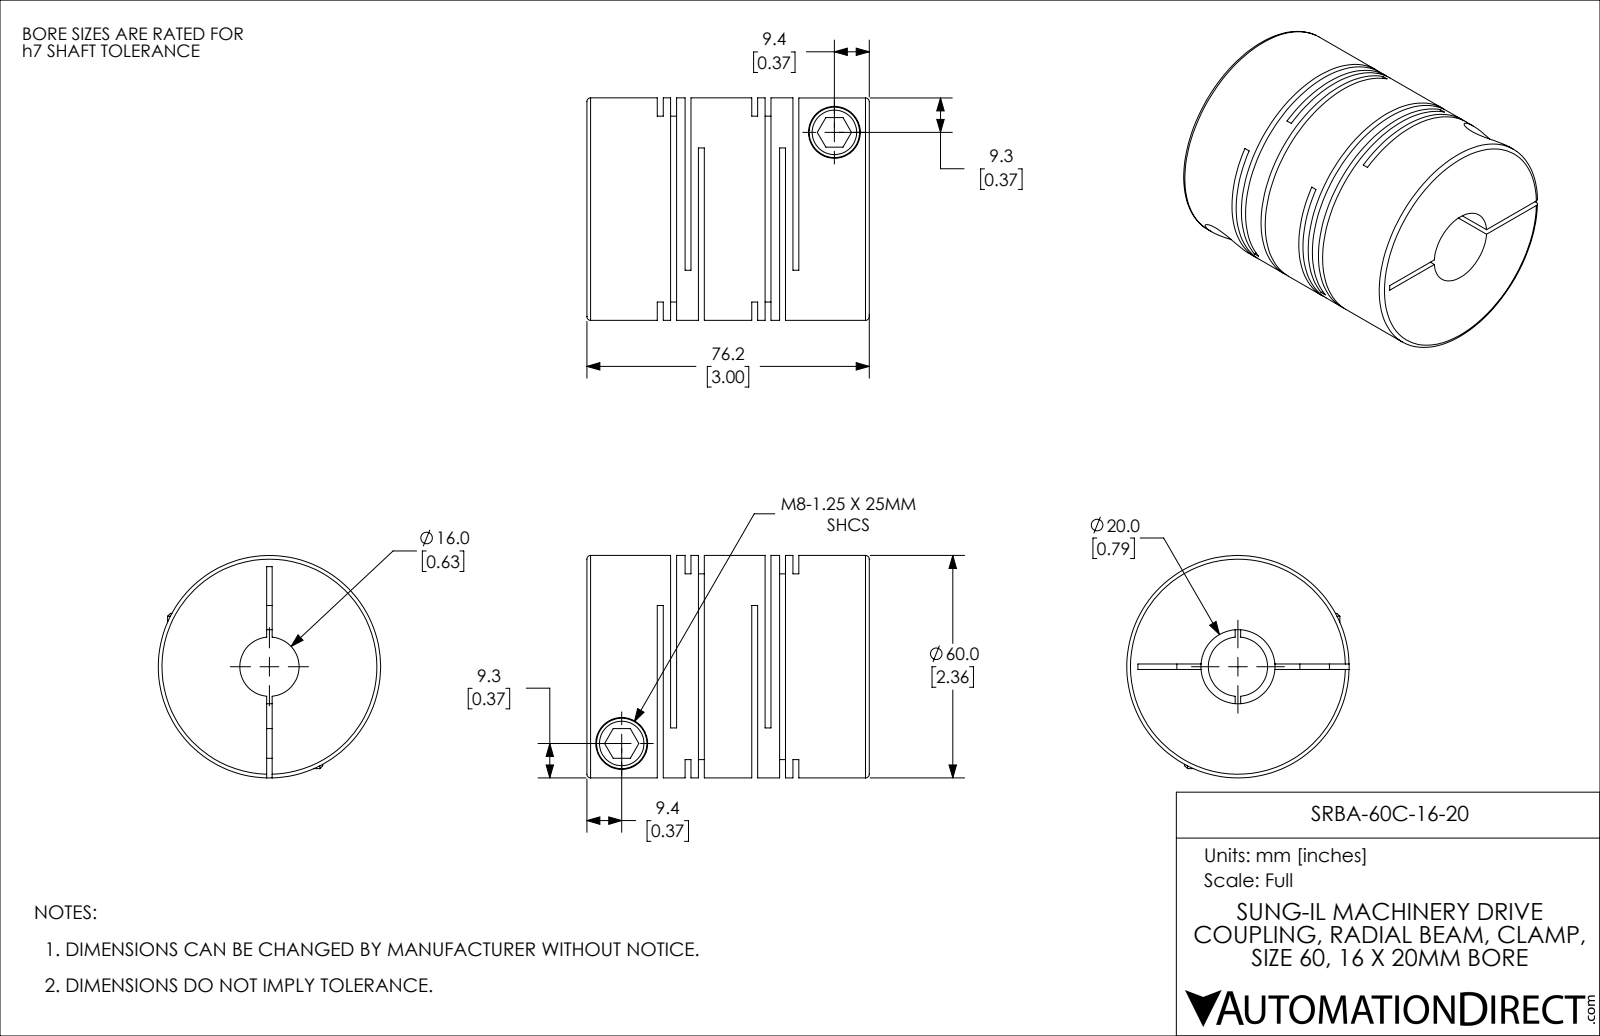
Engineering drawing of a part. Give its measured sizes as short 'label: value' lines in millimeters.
name: SRBA-60C-16-20
written by: SolidWorks 2021 (CONFIG_CONTROL_DESIGN)
unit: mm
bodies: 1 solid, 115 faces (60 planar, 42 cylindrical, 13 other)
size: 76.2 × 60 × 60
volume: 162 300 mm³; area: 59 250 mm²
holes: 2× ⌀8, 2× ⌀14, 1× ⌀16, 1× ⌀20
bosses: 2× ⌀13.6, 1× ⌀60
face distances: 1.6, 3.6, 7.5, 25.5, 33, 27.1, 5.9, 23.9, 18, 2
